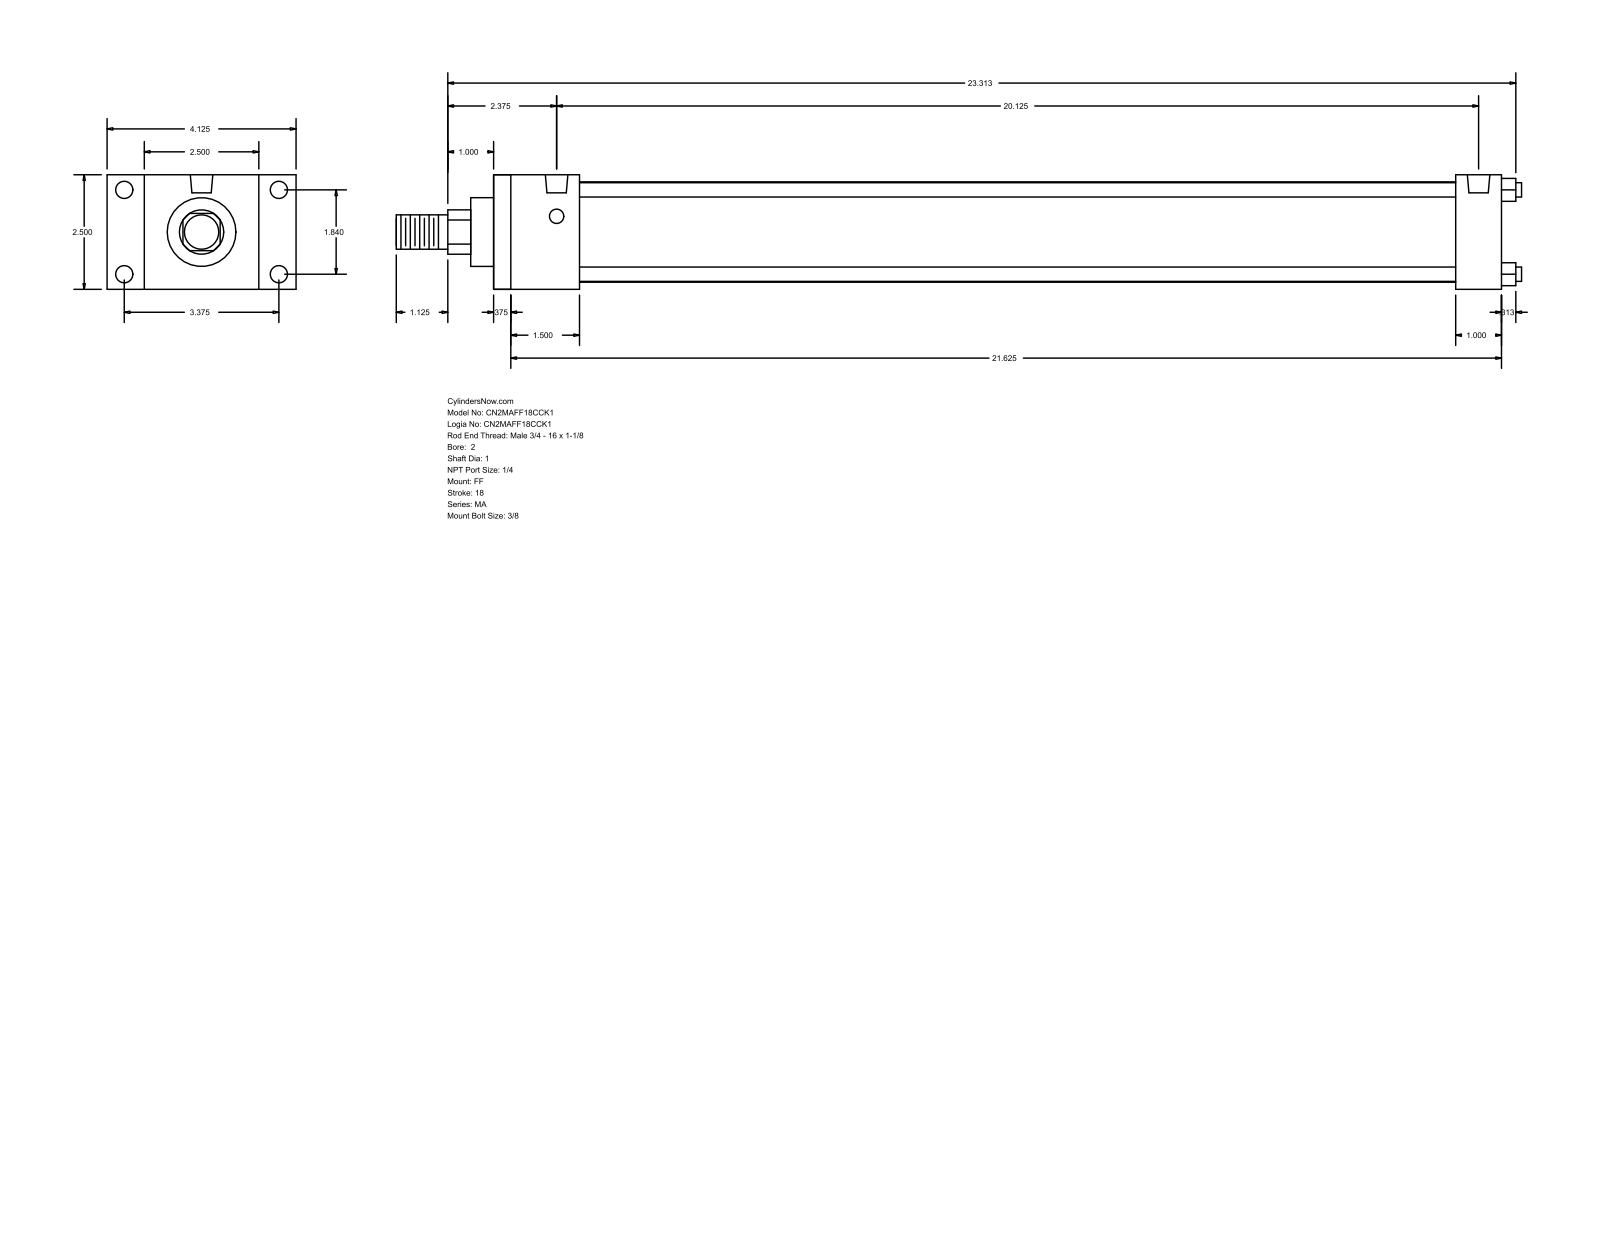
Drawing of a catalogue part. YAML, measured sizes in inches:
part_name: "MA_FF__0200_1"
step_written_by: "GSSL Pune (CONFIG_CONTROL_DESIGN)"
units: inches
bodies: {solids: 0, faces: 92, planar: 64, cylindrical: 28, other: 0}
overall_size: [24.563, 4.125, 2.5]
round_holes:
  - {diameter: 0.313, count: 4}
  - {diameter: 0.375, count: 4}
  - {diameter: 0.492, count: 2}
round_bosses_or_shafts:
  - {diameter: 0.313, count: 4}
  - {diameter: 2.19, count: 1}
  - {diameter: 1.5, count: 1}
  - {diameter: 1, count: 1}
  - {diameter: 0.75, count: 1}
partial_cylinders:
  - {radius: 0.484, count: 1}
face_to_face_distances: [2.5, 22, 0.375, 21.625, 1, 0.813, 0.5, 1.875, 21, 1.5]
hole_center_spacings: [1.84, 3.375, 3.844, 20.125]
